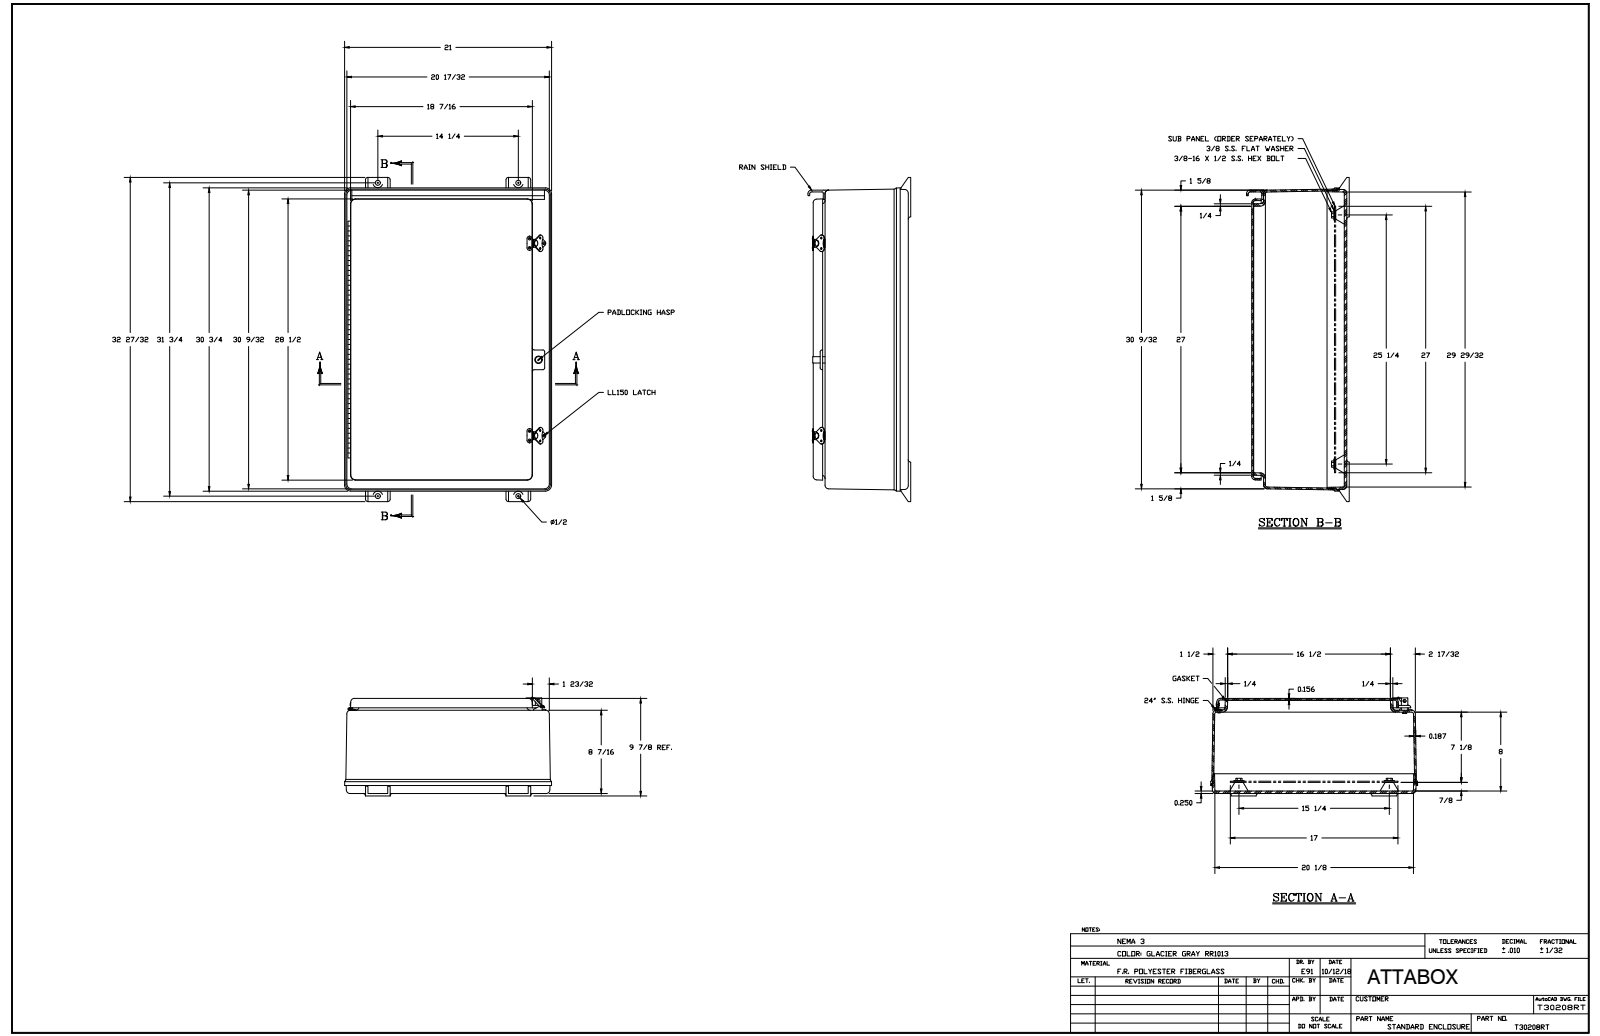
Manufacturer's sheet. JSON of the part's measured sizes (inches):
{"part_name": "T30208RT", "step_written_by": "SolidWorks 2018 (AUTOMOTIVE_DESIGN)", "units": "inches", "bodies": {"solids": 40, "faces": 1199, "planar": 475, "cylindrical": 476, "other": 248}, "overall_size": [32.844, 21, 10.437], "volume_in3": 491.4, "surface_area_in2": 5204, "round_holes": [[0.13, 25], [0.063, 8], [0.065, 6], [0.065, 5], [0.138, 4], [0.187, 4], [0.563, 4], [0.51, 2], [0.51, 2], [0.125, 1], [0.125, 1], [0.135, 1]], "round_bosses_or_shafts": [[0.297, 11], [0.14, 8], [0.5, 2], [0.25, 1], [0.201, 1], [0.2, 1], [0.135, 1]], "partial_cylinders_radius": [[0.01, 60], [0.25, 24], [0.375, 16], [0.187, 12], [0.5, 12], [0.188, 10], [0.03, 8], [0.125, 7]], "face_to_face_distances": [0.187, 0.25, 0.156, 9.625, 9.375, 9.469, 9.219, 8.437, 8.187, 1.032], "hole_center_spacings": [19.5, 0.938, 1.542, 7.5, 15.5, 0.858, 0.858, 2.486]}
